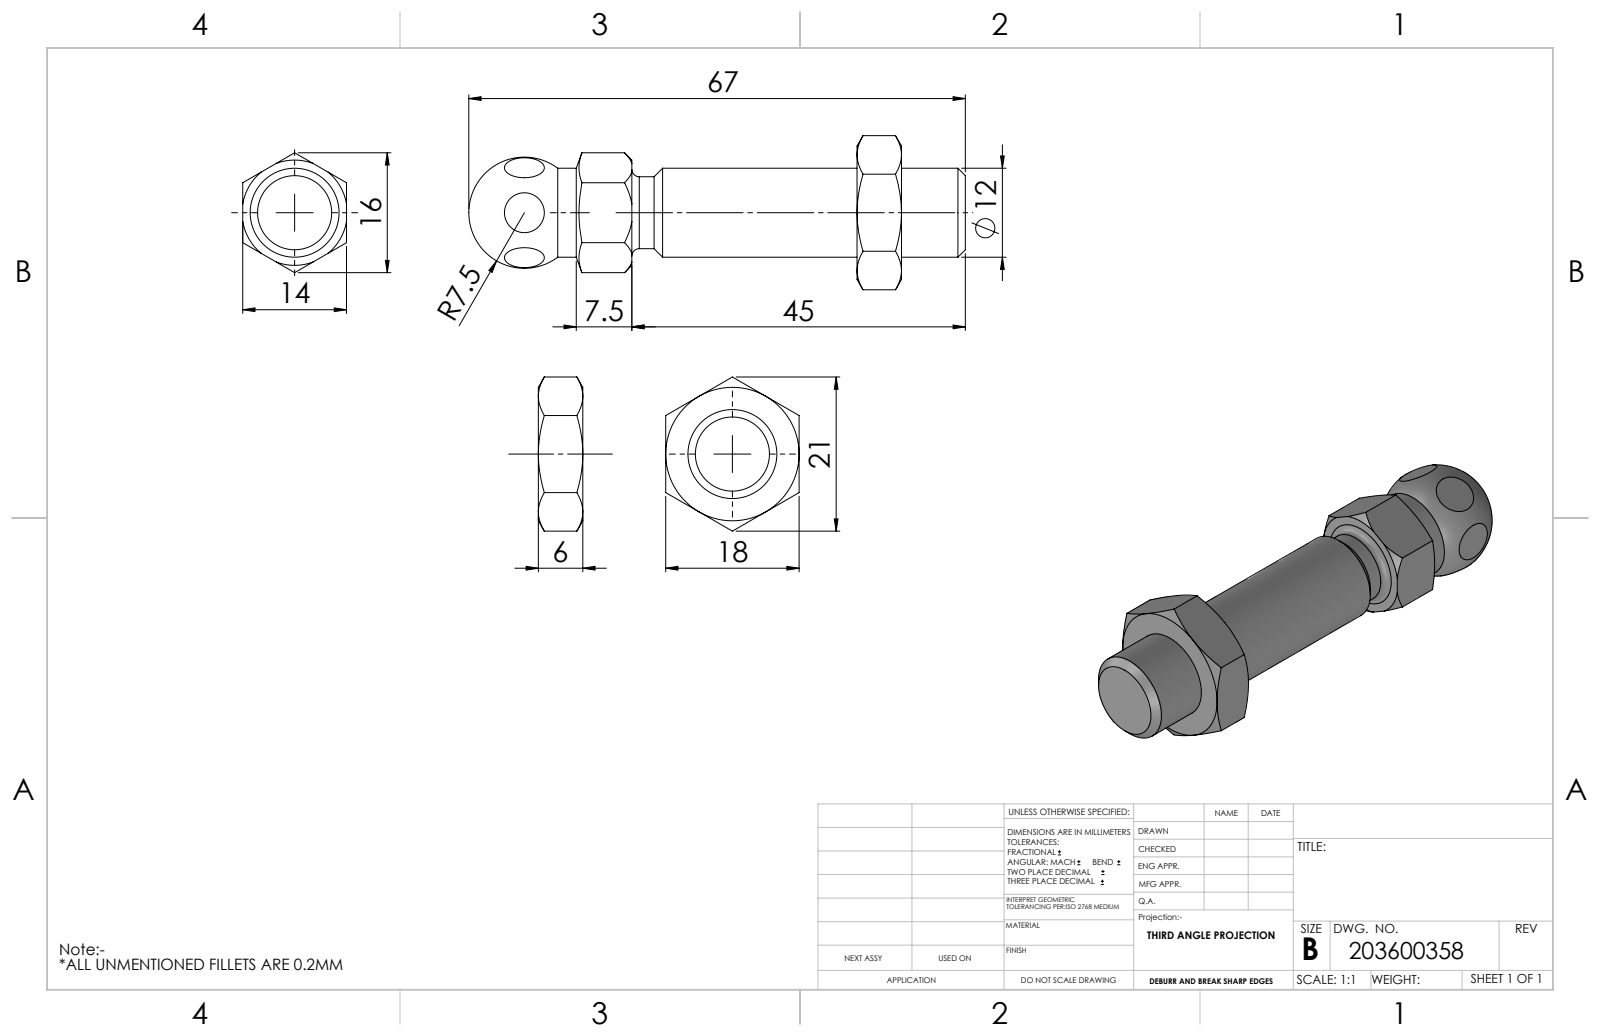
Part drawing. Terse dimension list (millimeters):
name: 203600358
written by: SolidWorks 2014 (AUTOMOTIVE_DESIGN)
unit: mm
bodies: 2 solids, 65 faces (22 planar, 10 cylindrical, 33 other)
size: 67 × 20.79 × 18
volume: 9 184 mm³; area: 3 817 mm²
holes: 1× ⌀10.2
bosses: 1× ⌀12, 1× ⌀9.7
face distances: 2, 16, 14, 18, 6, 14.61, 8.61, 30.39, 36.39, 45
